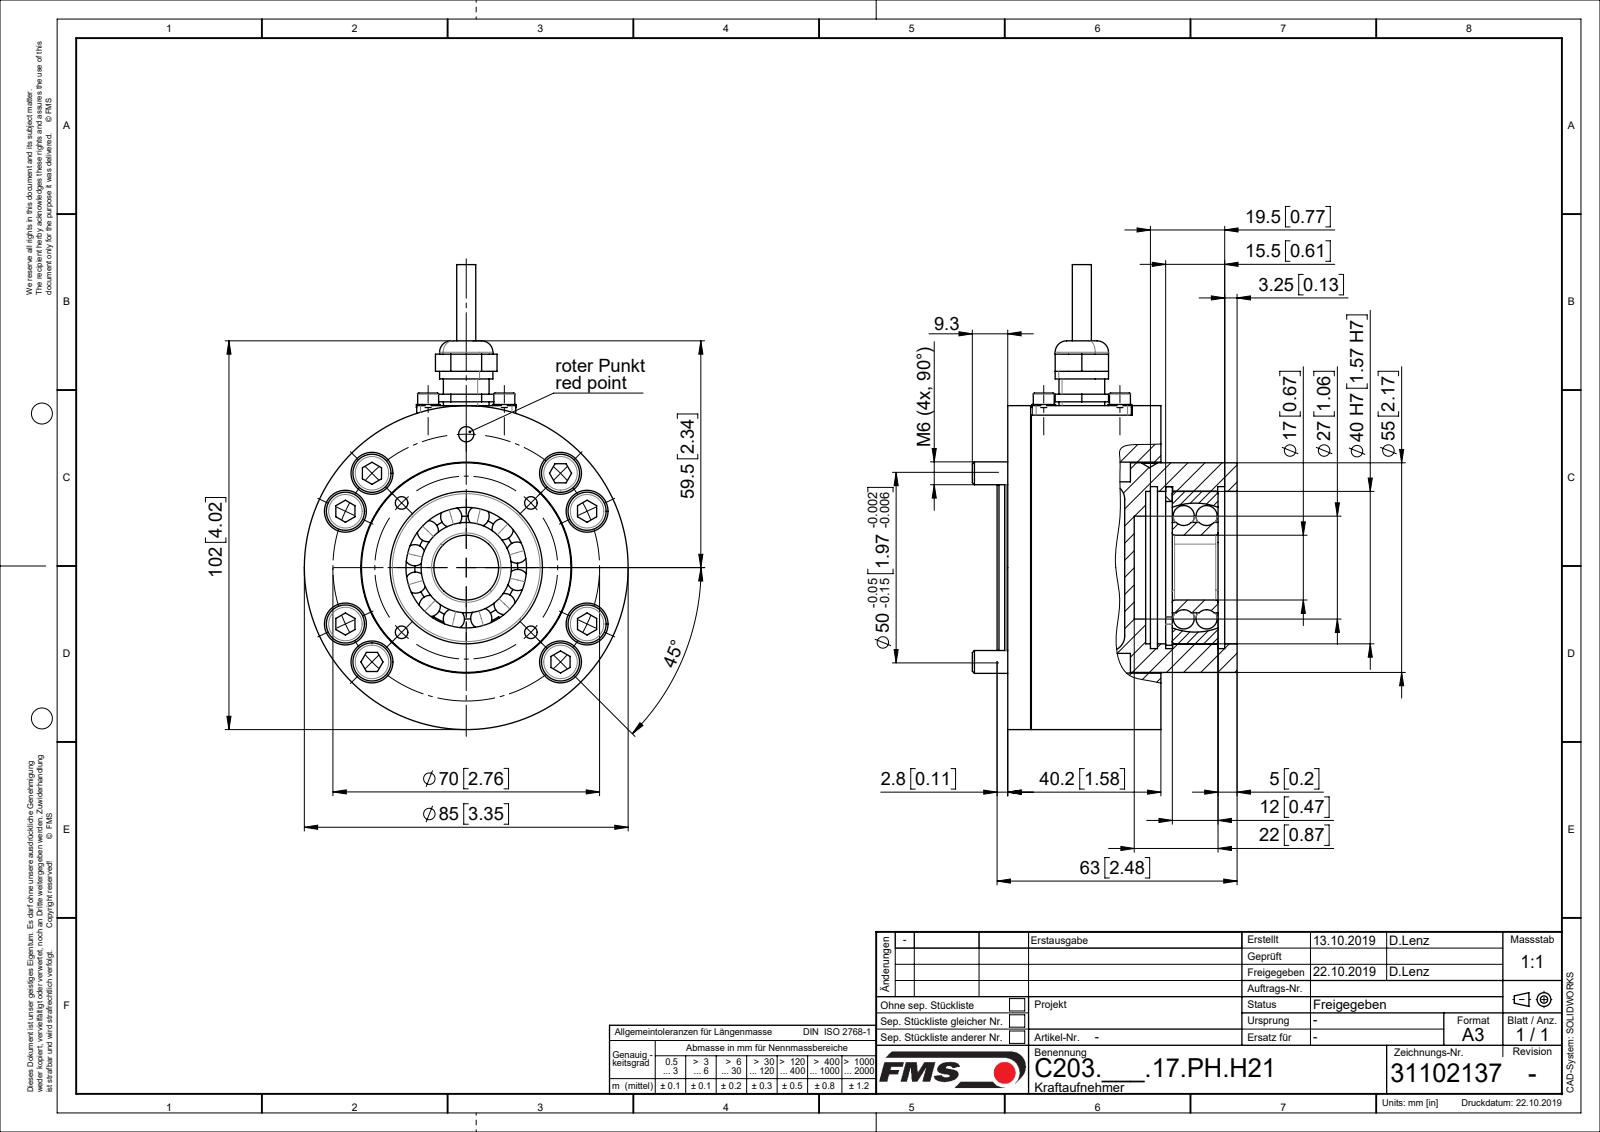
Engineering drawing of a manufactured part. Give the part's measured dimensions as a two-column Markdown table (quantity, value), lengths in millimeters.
| quantity | value |
| --- | --- |
| part name | ZEICHNUNG3; C0710091; C0709071; C0704203 (+8 more) |
| STEP written by | Mechanical Desktop 2009 (CONFIG_CONTROL_DESIGN) |
| units | millimeters |
| bodies | 27 solids, 557 faces (212 planar, 249 cylindrical, 96 other) |
| overall size | 100.5 × 85 × 72.35 |
| volume | 241 726 mm³ |
| surface area | 82 885 mm² |
| round holes (diameter × count) | 6.5 × 8, 11 × 8, 2.6 × 4, 3.2 × 4, 3.42 × 4, 5.15 × 4, 7 × 4, 4 × 1, 6 × 1, 10.68 × 1, 15 × 1, 17 × 1 |
| round bosses / shafts (diameter × count) | 10 × 8, 6 × 8, 1.5 × 5, 6.2 × 4, 5.5 × 4, 5 × 4, 3 × 4, 85 × 1 |
| partial cylindrical surfaces (radius × count) | 2.5 × 4, 5 × 2 |
| main face-to-face distances | 6, 3, 40, 34, 4, 43, 24.5, 9, 58, 15 |
| hole center spacings | 35, 42.44, 20, 11, 12.16, 14.14, 14.91, 24 |
